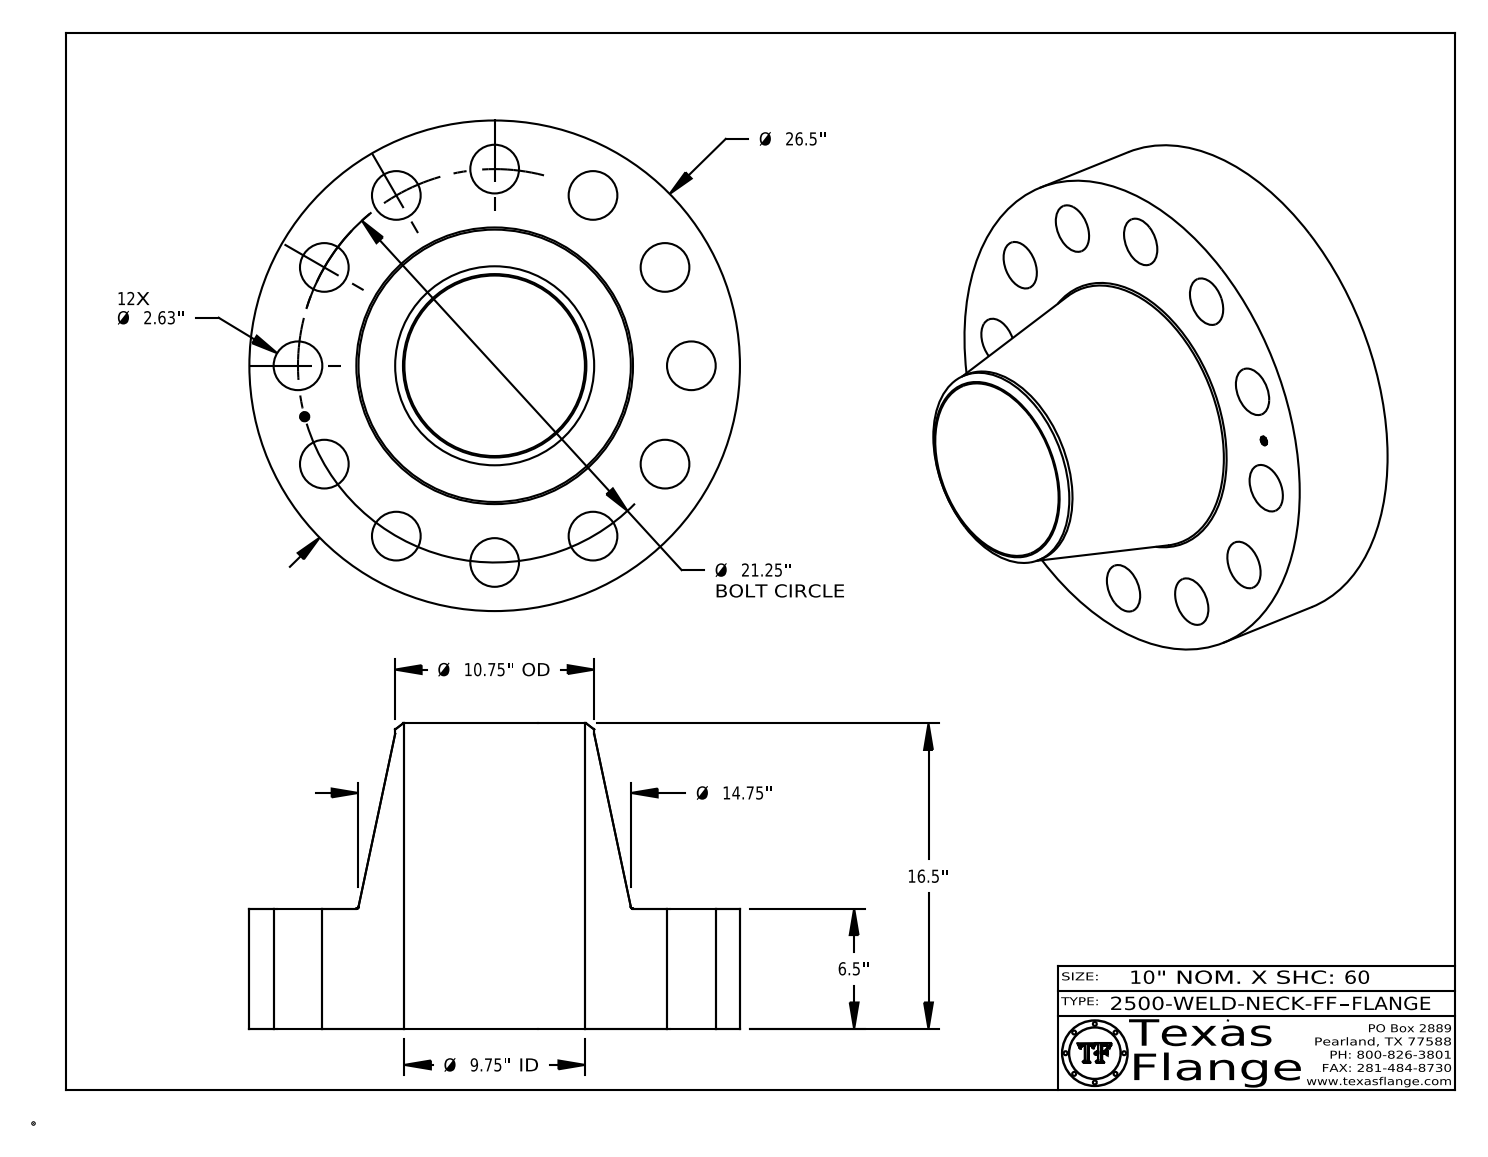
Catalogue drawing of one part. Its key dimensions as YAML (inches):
part_name: "2500-WELD-NECK-FF"
step_written_by: "CATIA V5 STEP AP214 (AUTOMOTIVE_DESIGN)"
units: inches
bodies: {solids: 1, faces: 424, planar: 368, cylindrical: 50, other: 6}
overall_size: [26.5, 26.5, 16.5]
volume: 3193
surface_area: 2831
round_holes:
  - {diameter: 2.63, count: 12}
  - {diameter: 0.495, count: 1}
  - {diameter: 9.75, count: 1}
round_bosses_or_shafts:
  - {diameter: 0.03, count: 8}
  - {diameter: 26.5, count: 1}
  - {diameter: 10.75, count: 1}
  - {diameter: 0.39, count: 1}
face_to_face_distances: [6.5, 16.5, 10, 6.485, 0.015, 10.015, 0.148, 0.144, 0.027, 0.096]
hole_center_spacings: [10.625, 5.5, 18.403, 15.026, 20.526, 15.026, 20.526, 21.25]
